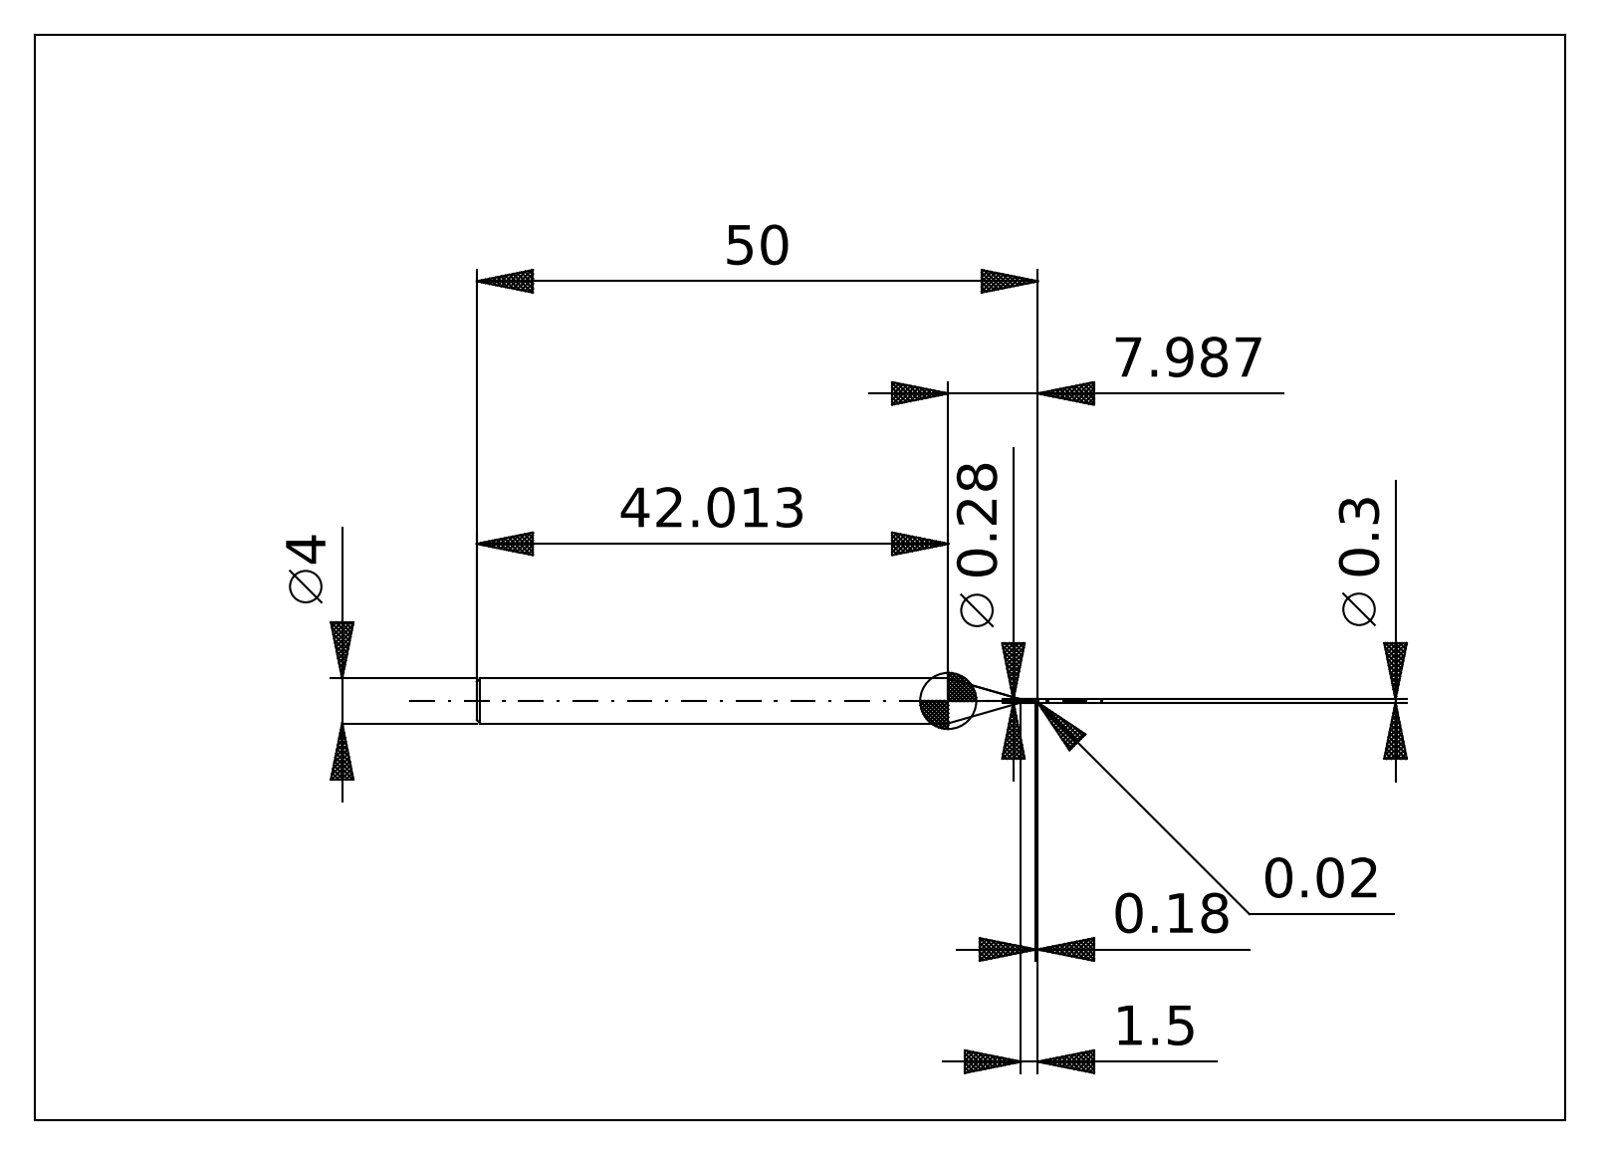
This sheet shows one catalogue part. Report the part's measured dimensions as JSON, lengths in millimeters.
{"step_written_by": "ACIS (automotive_design)", "units": "millimeters", "bodies": {"solids": 2, "faces": 26, "planar": 6, "cylindrical": 8, "other": 12}, "overall_size": [50, 4, 4], "volume_mm3": 557, "surface_area_mm2": 585, "round_bosses_or_shafts": [[4, 1], [0.28, 1]], "face_to_face_distances": [50, 49.96, 49.82, 7.99, 7.95, 7.81, 42.01]}
